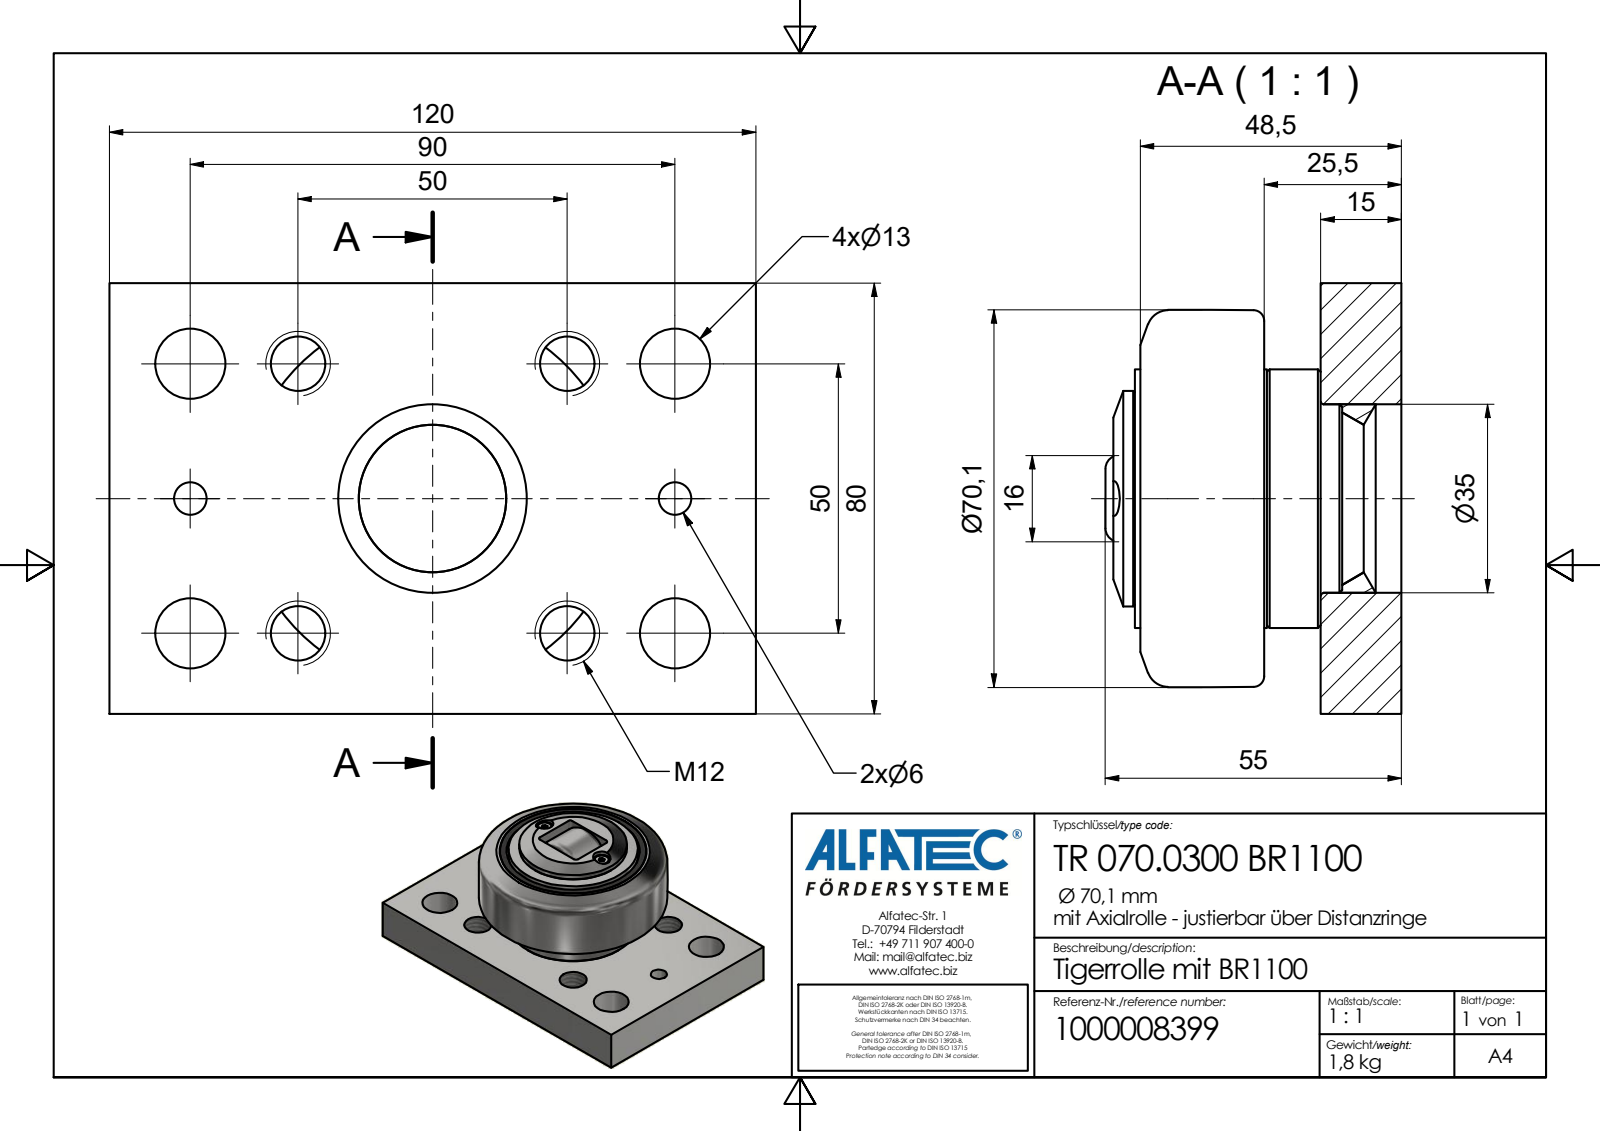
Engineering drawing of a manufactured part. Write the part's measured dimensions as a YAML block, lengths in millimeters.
part_name: "TR 070.0300 BR1100_Kontur"
step_written_by: "Autodesk Inventor 2020 (AP242_MANAGED_MODEL_BASED_3D_ENGINEERING_MIM_LF)"
units: millimeters
bodies: {solids: 1, faces: 114, planar: 45, cylindrical: 45, other: 24}
overall_size: [120, 80, 55]
volume: 235191
surface_area: 41505
round_holes:
  - {diameter: 10.11, count: 4}
  - {diameter: 13, count: 4}
  - {diameter: 3.5, count: 2}
  - {diameter: 6, count: 2}
  - {diameter: 6.5, count: 2}
  - {diameter: 25, count: 1}
  - {diameter: 35, count: 1}
  - {diameter: 35.2, count: 1}
round_bosses_or_shafts:
  - {diameter: 5.35, count: 2}
  - {diameter: 3, count: 2}
  - {diameter: 48, count: 1}
  - {diameter: 40, count: 1}
partial_cylinders:
  - {radius: 1, count: 4}
  - {radius: 5.1, count: 1}
  - {radius: 5.5, count: 1}
  - {radius: 6.5, count: 1}
  - {radius: 8, count: 1}
  - {radius: 12.47, count: 1}
face_to_face_distances: [15, 80, 25.5, 10.5, 120, 49.5, 34.5, 24, 48.5, 1]
hole_center_spacings: [50, 20, 25, 26.93, 32.02, 35.36, 39.05, 47.17]
